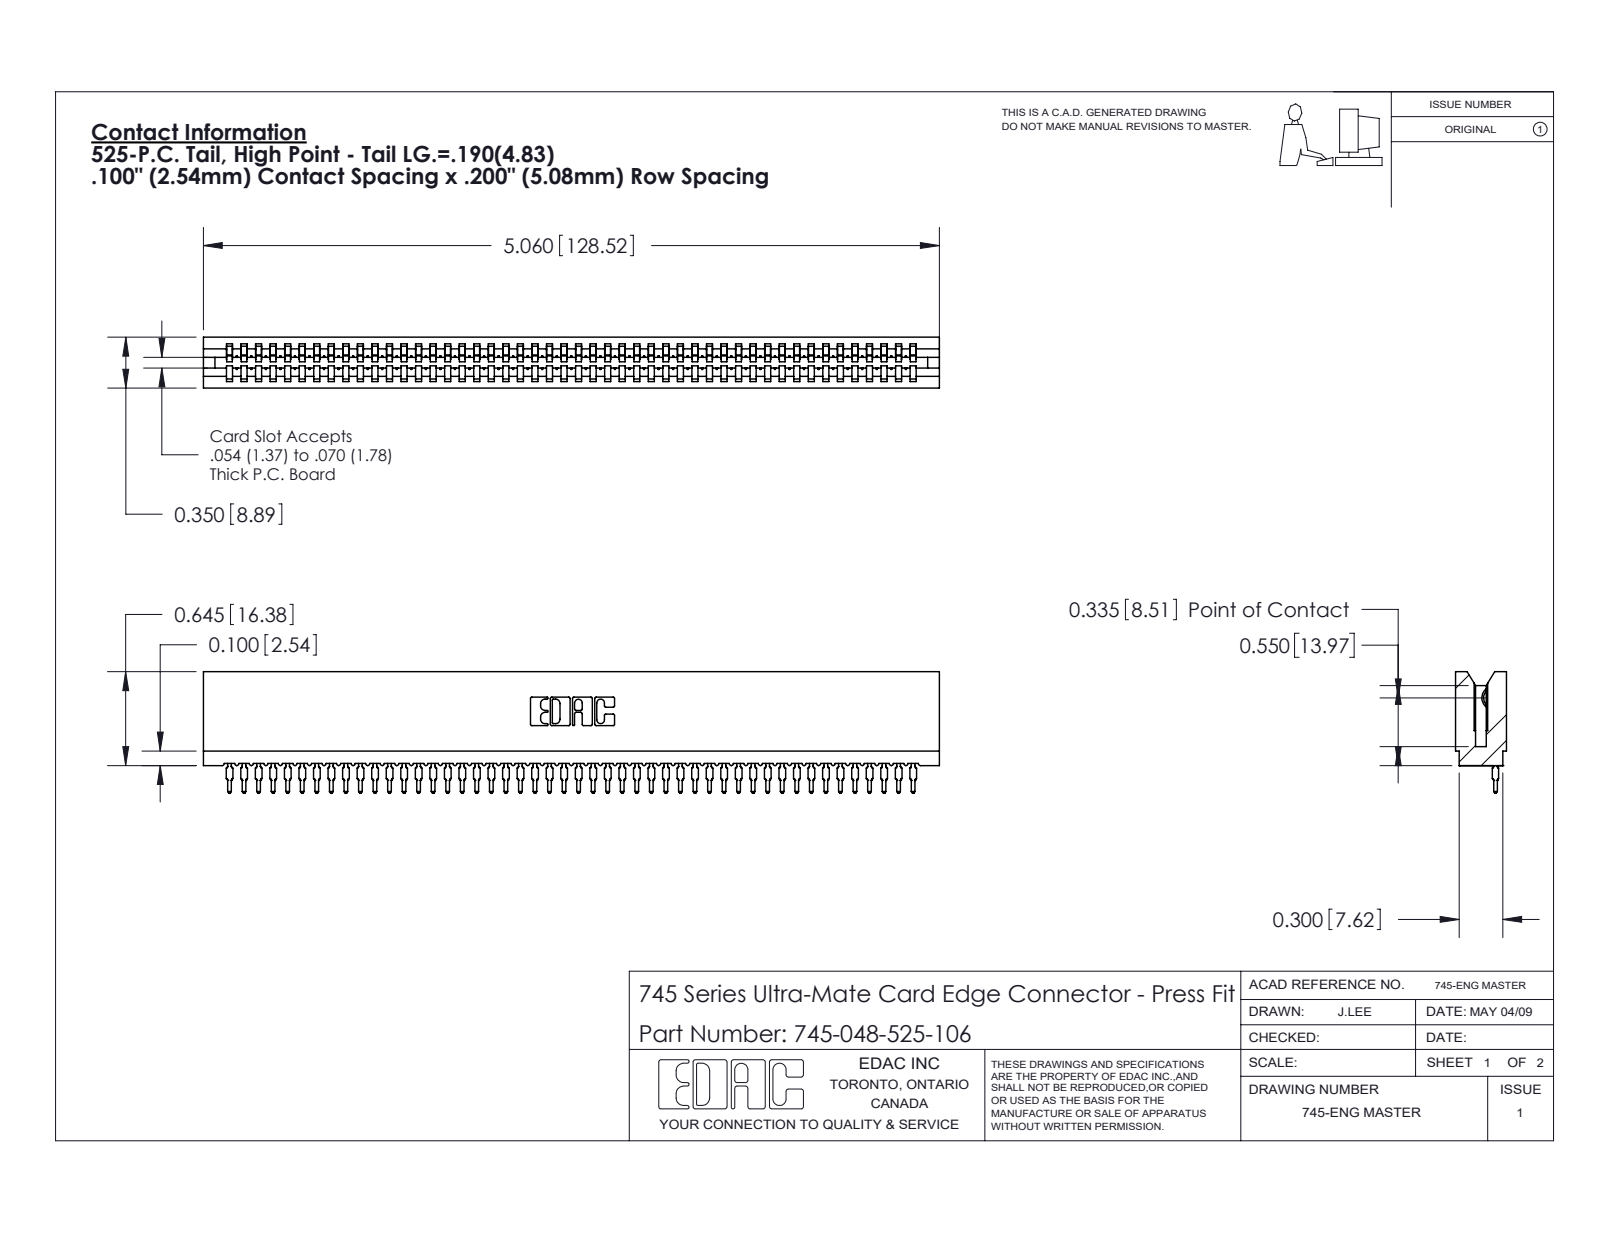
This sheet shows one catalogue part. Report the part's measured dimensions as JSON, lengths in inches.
{"part_name": "745 Part_Insulator Option - 06; 745-292-001_525; 745-048-525-106", "step_written_by": "SolidWorks 2020 (CONFIG_CONTROL_DESIGN)", "units": "inches", "bodies": {"solids": 49, "faces": 5472, "planar": 3272, "cylindrical": 952, "other": 1248}, "overall_size": [5.06, 0.836, 0.35], "volume_in3": 0.673, "surface_area_in2": 31.93, "partial_cylinders_radius": [[0.015, 96], [0.021, 96], [0.01, 22], [0.007, 6], [0.031, 6], [0.005, 4], [0.011, 4], [0.026, 3]], "face_to_face_distances": [0.35, 0.045, 0.305, 0.138, 0.212, 0.093, 0.167, 0.063, 0.287, 0.243]}
